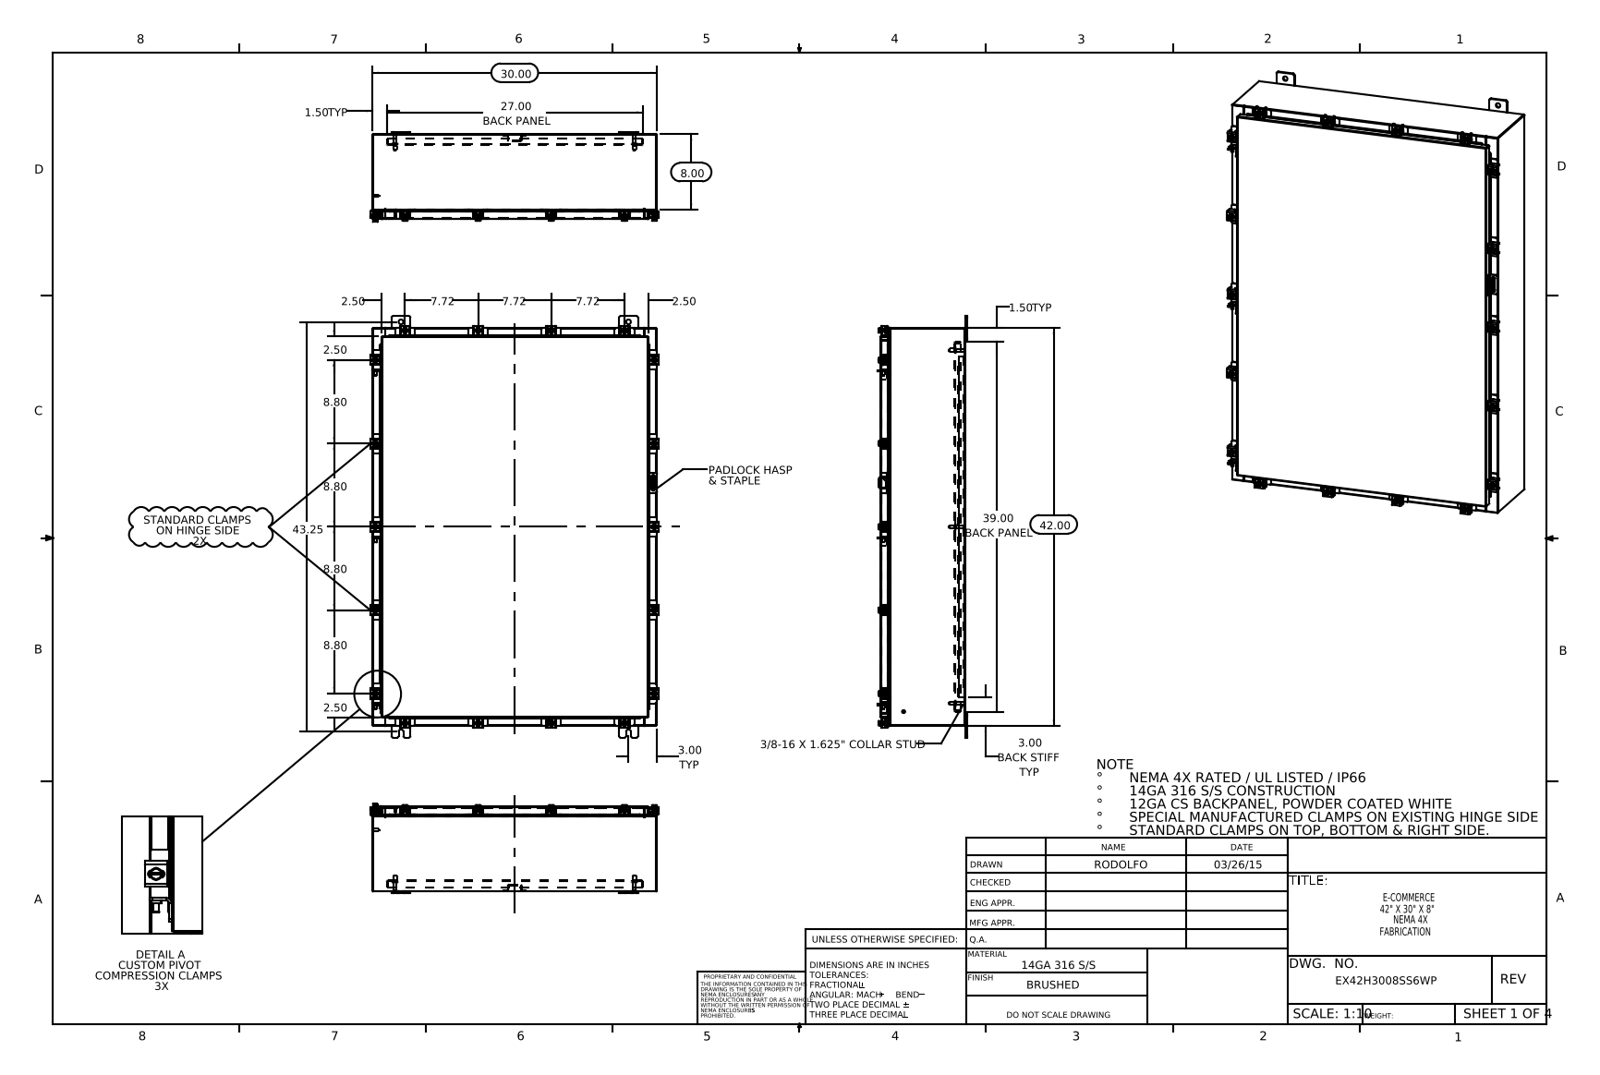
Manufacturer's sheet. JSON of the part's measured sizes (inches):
{"part_name": "EX42H3008SS6WP Body; Special Clamp Assembly; EX42H3008SS6WP Special Clamp; 22101002_RTP29 (+8 more)", "step_written_by": "SolidWorks 2014 (CONFIG_CONTROL_DESIGN)", "units": "inches", "bodies": {"solids": 116, "faces": 2878, "planar": 1525, "cylindrical": 1123, "other": 230}, "overall_size": [44.5, 30.421, 9.453], "volume_in3": 437.9, "surface_area_in2": 10823, "round_holes": [[0.213, 18], [0.26, 18], [0.5, 10], [0.125, 1], [0.25, 1]], "round_bosses_or_shafts": [[0.5, 18], [0.25, 18], [0.399, 15], [0.625, 6], [0.375, 6], [0.33, 6], [0.315, 2], [0.236, 2]], "partial_cylinders_radius": [[0.06, 76], [0.141, 36], [0.12, 33], [0.013, 30], [0.09, 27], [0.088, 26], [0.05, 25], [0.145, 24]], "face_to_face_distances": [0.075, 8.9, 8.826, 8.975, 0.104, 1, 1.075, 7.826, 7.9, 1.179], "hole_center_spacings": [30.737, 29.451, 2.347, 4.44, 8.798, 17.719, 18.625, 20.752]}
